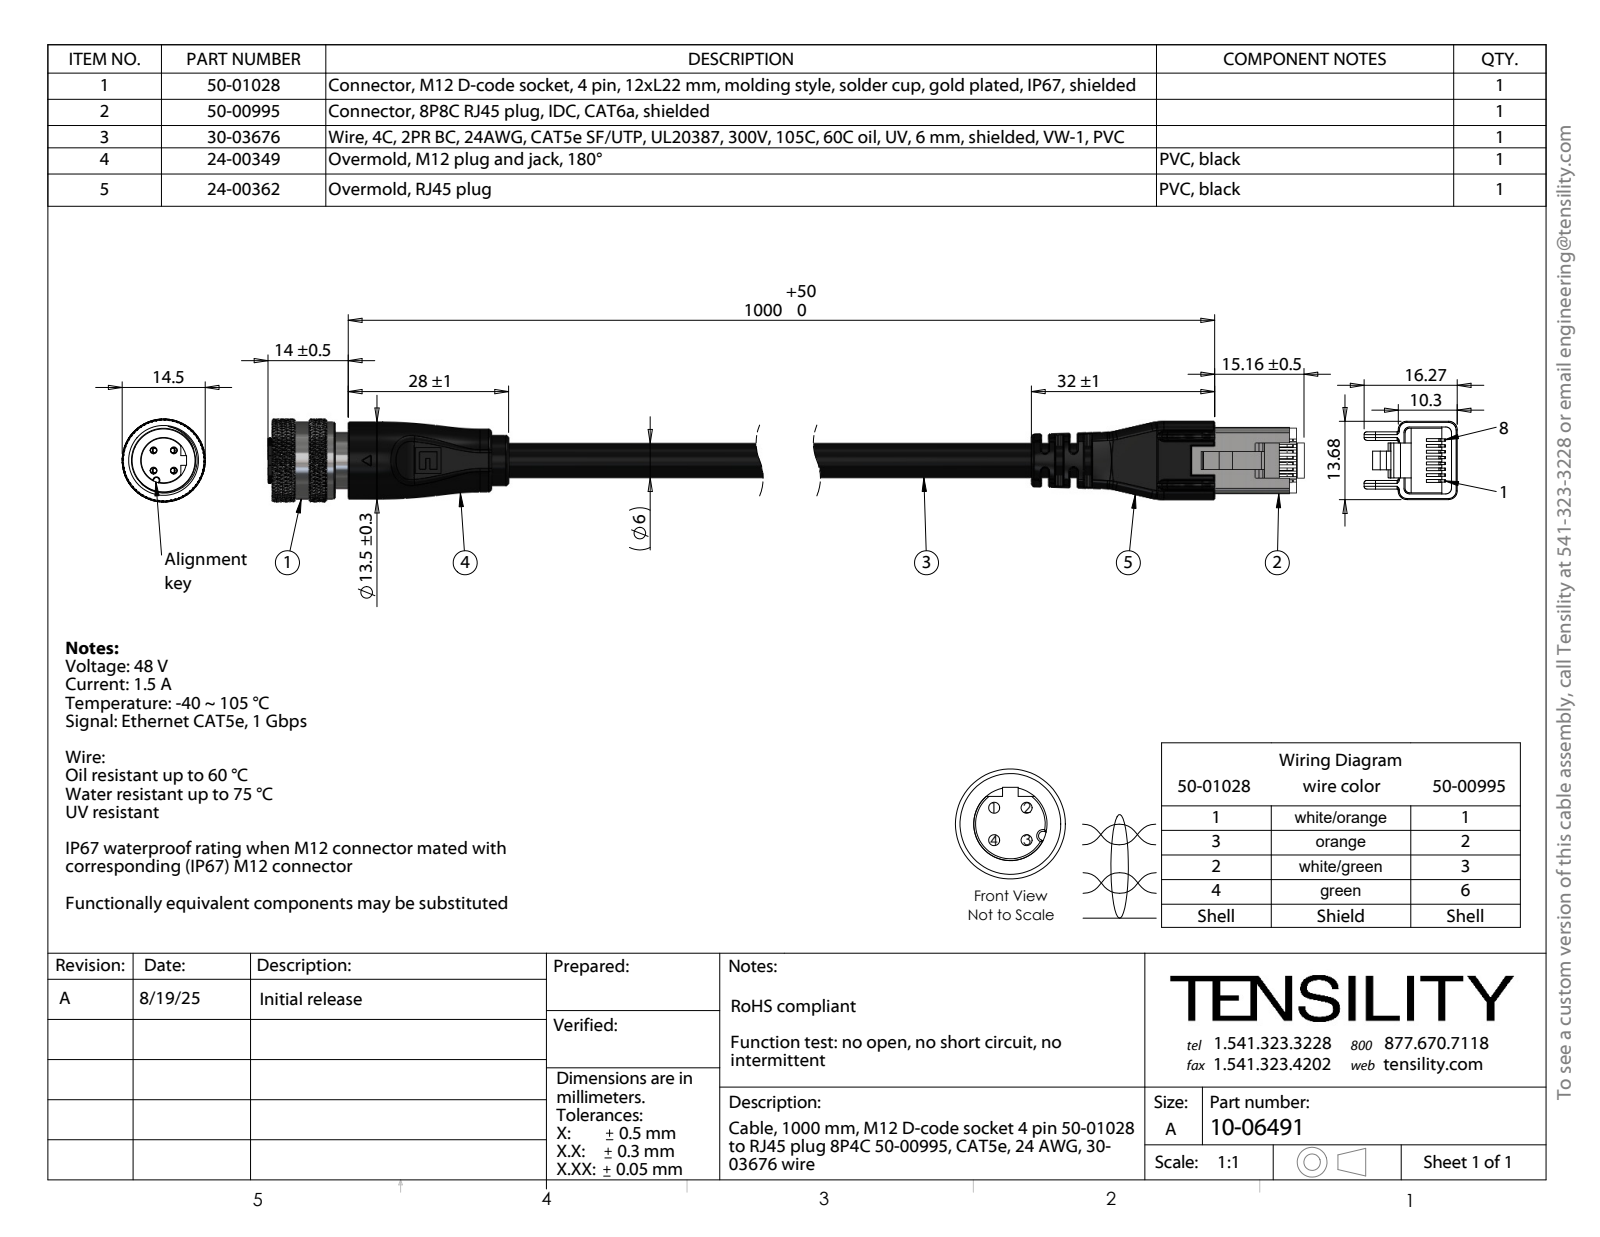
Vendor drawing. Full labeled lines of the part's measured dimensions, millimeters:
Part name (STEP PRODUCT): 10-06491; 50-01028-03_默认; 50-01028-01_默认; 50-01028-05_默认 (+7 more)
STEP written by: SolidWorks 2025 (CONFIG_CONTROL_DESIGN)
Units: millimetres
Bodies: 55 solids, 3967 faces (546 planar, 928 cylindrical, 2493 other)
Overall size (bounding box): 229.11 × 18.37 × 14.5
Volume: 14 248 mm³ · Surface area: 29 704 mm²
Round holes (diameter × count): ⌀0.2 ×28, ⌀1.05 ×4, ⌀1.1 ×4, ⌀1.2 ×4, ⌀3.16 ×1, ⌀3.21 ×1, ⌀3.56 ×1, ⌀9 ×1, ⌀10 ×1, ⌀11.2 ×1
Round bosses / shafts (diameter × count): ⌀1.6 ×4, ⌀1.5 ×4, ⌀13.5 ×1, ⌀11 ×1, ⌀10.6 ×1, ⌀10.5 ×1, ⌀9.8 ×1, ⌀9.7 ×1
Partial cylindrical surfaces — rounded edges, fillets, slot ends (radius × count): R0.2 ×11, R0.1 ×10, R0.5 ×10, R1.5 ×10, R0.62 ×8, R0.4 ×6, R1 ×5, R10 ×4
Main face-to-face distances: 1.25, 1, 2.5, 3.75, 9.3, 5, 1.5, 199.5, 12.68, 8.5
Hole centre spacings: 1.91, 0.36, 2.09, 1.06, 0.89, 1.08, 1.24, 1.8
